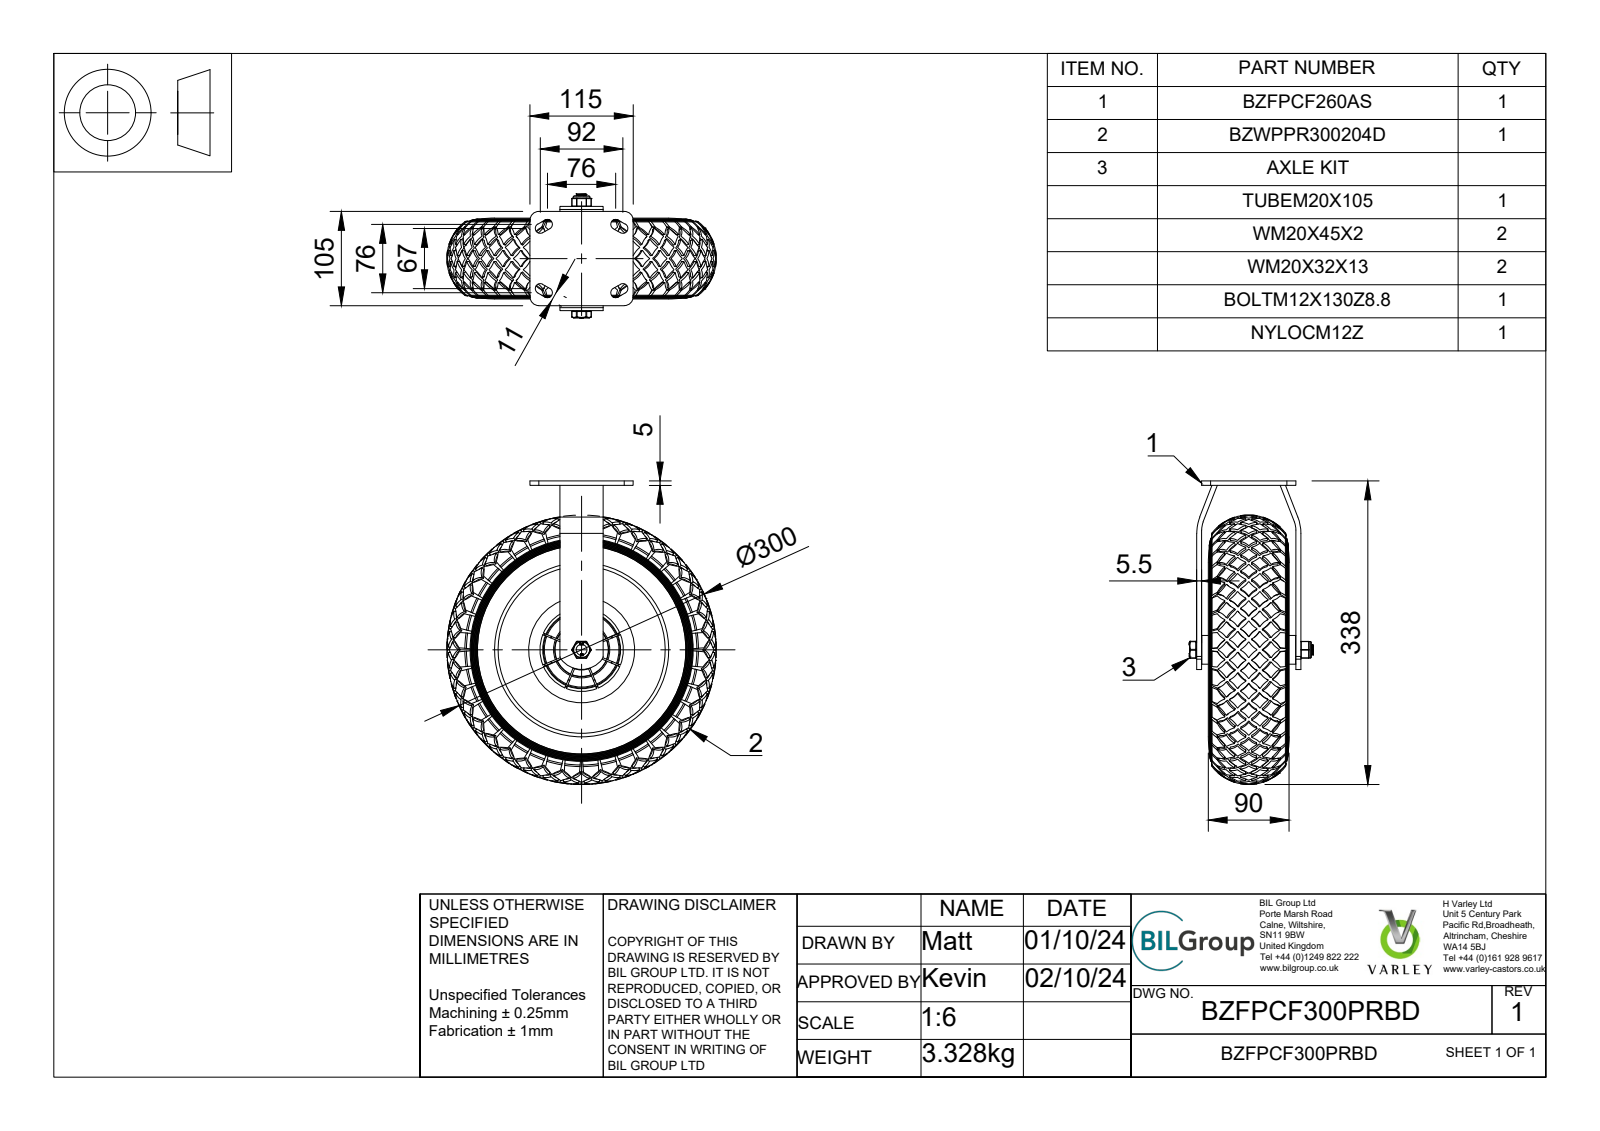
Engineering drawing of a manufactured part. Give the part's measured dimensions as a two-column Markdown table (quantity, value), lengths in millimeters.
| quantity | value |
| --- | --- |
| part name | BZFPCF300PRBD v5; BZFPCF260AS v1; BZFPCF260AS; FABRICATED STEEL BRACKET (+8 more) |
| STEP written by | Autodesk Translation Framework v13.20.0.188 (AUTOMOTIVE_DESIGN) |
| units | millimeters |
| bodies | 25 solids, 2155 faces (528 planar, 618 cylindrical, 1009 other) |
| overall size | 338 × 300 × 138.3 |
| volume | 1 529 000 mm³ |
| surface area | 964 772 mm² |
| round holes (diameter × count) | 0.8 × 2, 12 × 2, 12.5 × 1, 13 × 1, 14 × 1, 20 × 1, 20.8 × 1, 21 × 1, 59.25 × 1, 60 × 1, 100.25 × 1 |
| round bosses / shafts (diameter × count) | 7.5 × 9, 100 × 1, 66 × 1, 63.25 × 1, 45 × 1, 44 × 1, 38.5 × 1, 35 × 1 |
| partial cylindrical surfaces (radius × count) | 0.5 × 264, 24.59 × 160, 0.93 × 16, 5.5 × 8, 1 × 6, 0.4 × 4, 0.77 × 4, 10 × 4 |
| main face-to-face distances | 5.5, 110.5, 5, 2, 79, 22.5, 93.5, 17, 88, 11 |
| hole center spacings | 7.55, 22.7, 2.98, 30.05 |
